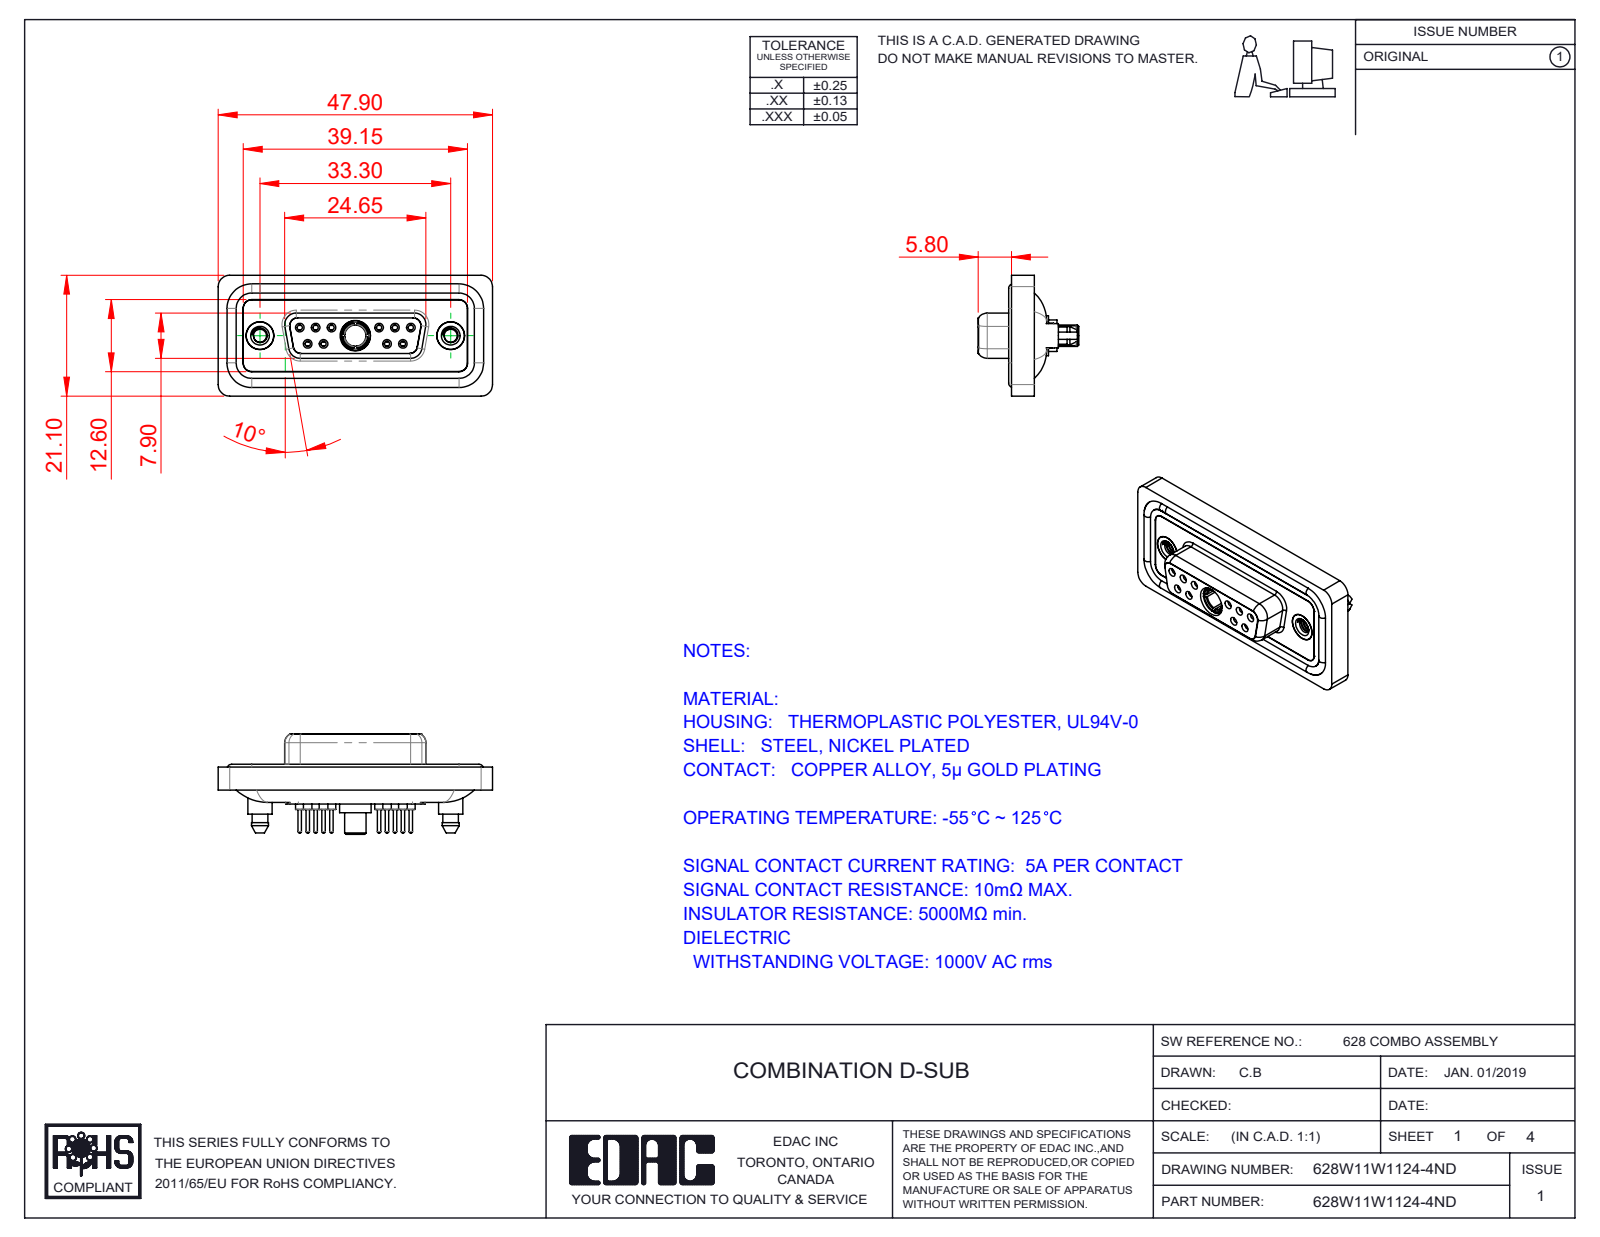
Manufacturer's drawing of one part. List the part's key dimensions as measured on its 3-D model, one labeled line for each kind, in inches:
Part name (STEP PRODUCT): 628Combo Contact Row 1_24; 628W11W1124-4ND; 628Combo Shell Rear_15 Contacts; 628Combo Threaded Boardlock_D (+5 more)
STEP written by: SolidWorks 2020 (CONFIG_CONTROL_DESIGN)
Units: inches
Bodies: 19 solids, 1076 faces (300 planar, 449 cylindrical, 327 other)
Overall size (bounding box): 1.886 × 0.831 × 0.691
Volume: 0.383 in³ · Surface area: 16.09 in²
Round holes (diameter × count): ⌀0.035 ×10, ⌀0.043 ×10, ⌀0.059 ×10, ⌀0.079 ×10, ⌀0.067 ×6, ⌀0.063 ×4, ⌀0.191 ×3, ⌀0.089 ×2, ⌀0.157 ×2, ⌀0.159 ×2, ⌀0.197 ×2, ⌀0.146 ×1
Round bosses / shafts (diameter × count): ⌀0.087 ×10, ⌀0.063 ×10, ⌀0.024 ×10, ⌀0.213 ×2, ⌀0.195 ×2, ⌀0.189 ×2, ⌀0.167 ×2, ⌀0.217 ×1
Partial cylindrical surfaces — rounded edges, fillets, slot ends (radius × count): R0.059 ×24, R0.079 ×20, R0.053 ×12, R0.063 ×10, R0.01 ×4, R0.02 ×4, R0.024 ×4, R0.026 ×4
Main face-to-face distances: 0.016, 0.063, 0.071, 0.114, 0.02, 0.043, 0.222, 0.293, 0.26, 0.278
Hole centre spacings: 0.124, 0.109, 0.545, 0.436, 0.654, 0.198, 0.198, 0.218
